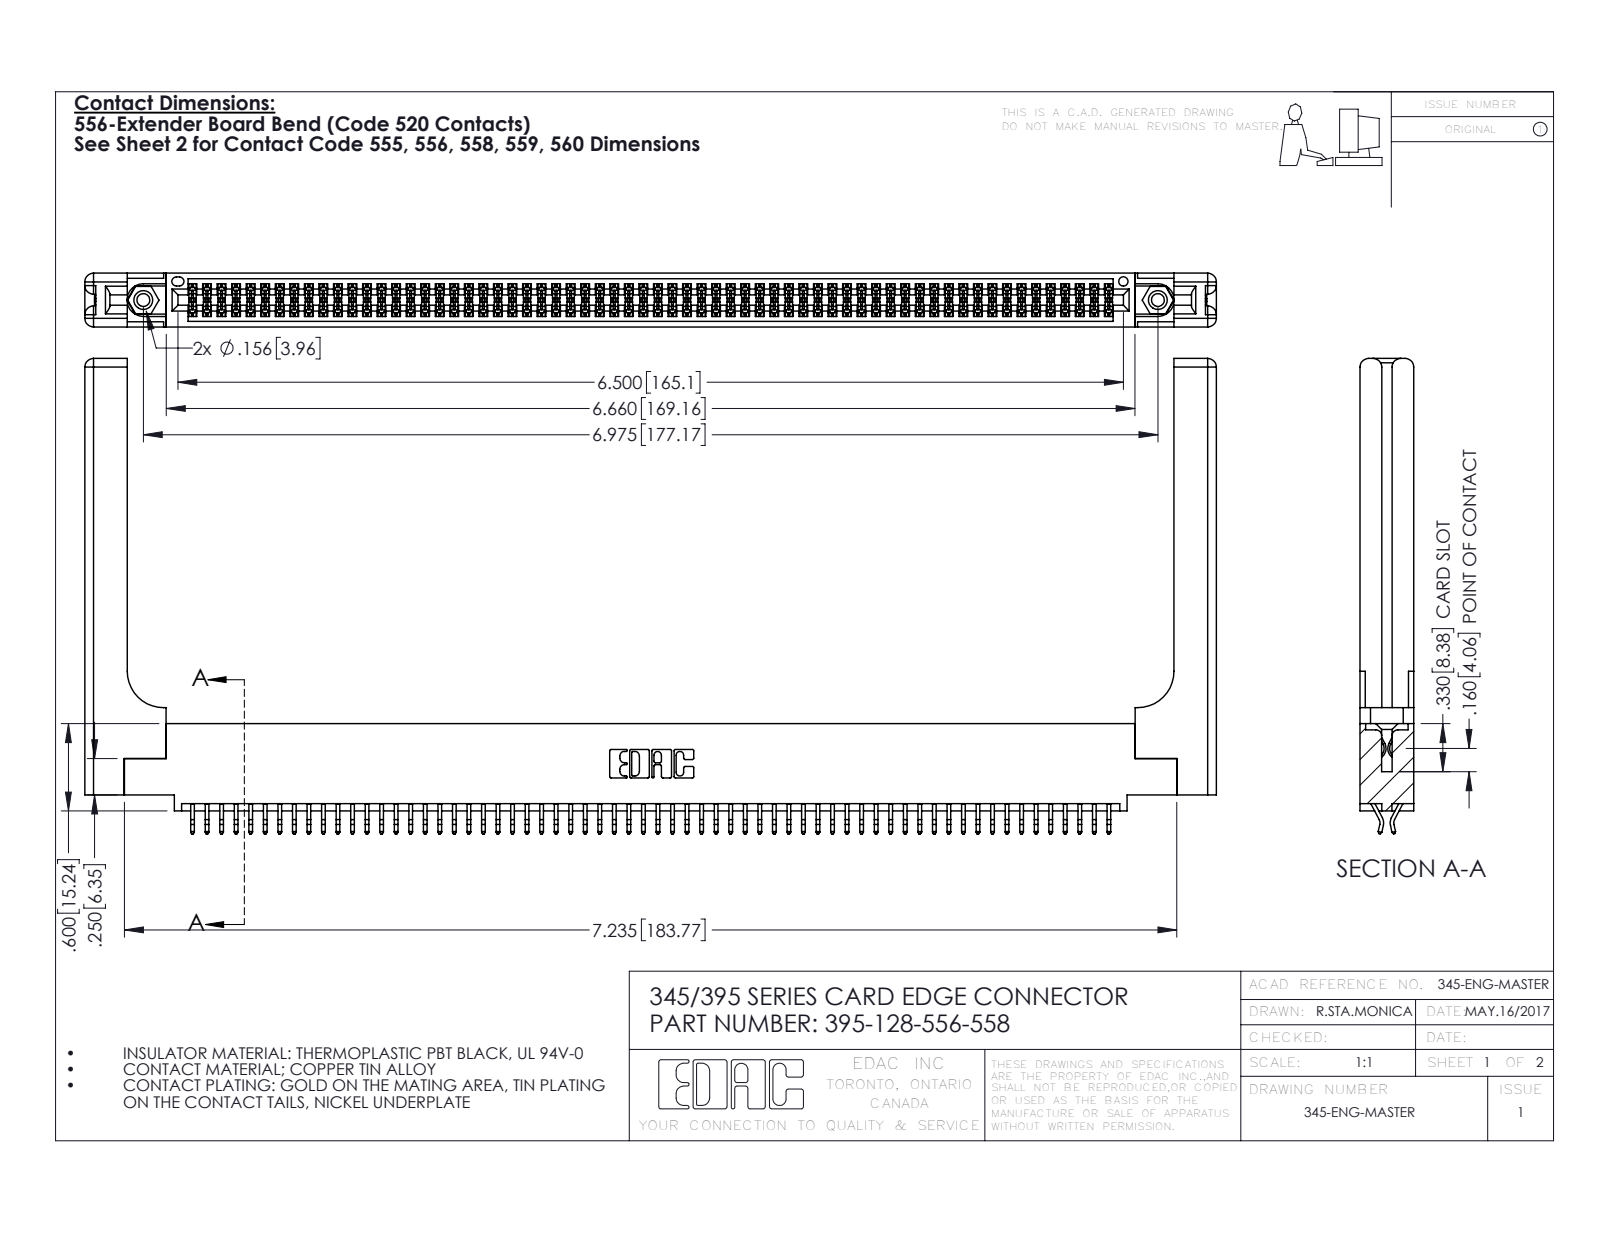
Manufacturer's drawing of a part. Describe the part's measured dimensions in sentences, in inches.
The part is named "345-220-058_345-220-058; 395-128-556-558; 345-250-001_345-250-001-102; 345 Part_0.110 Offset - 0.156 Dia-TH (+1 more)". Its 3-D file was written by "SolidWorks 2016 (CONFIG_CONTROL_DESIGN)". It is 133 solids with 7554 faces: 4968 planar, 2526 cylindrical and 60 other. Overall it measures 7.779 by 3.267 by 0.37 inches. Its volume is 1.696 cubic inches and its surface area 52.74 square inches. Round holes: 2 of diameter 0.089, 2 of diameter 0.125, 2 of diameter 0.156, 1 of diameter 0.064. Round bosses or shafts: 2 of diameter 0.155. Partial cylindrical surfaces (rounded edges, fillets, slot ends): 192 of radius 0.006, 22 of radius 0.01, 16 of radius 0.06, 6 of radius 0.007, 6 of radius 0.031, 3 of radius 0.026, 2 of radius 0.01, 2 of radius 0.014. The main face-to-face distances are 0.072, 0.298, 0.37, 0.025, 0.098, 0.272, 0.2, 0.225, 0.148, 0.15. The hole center spacings are 0.27, 6.739, 6.975.
